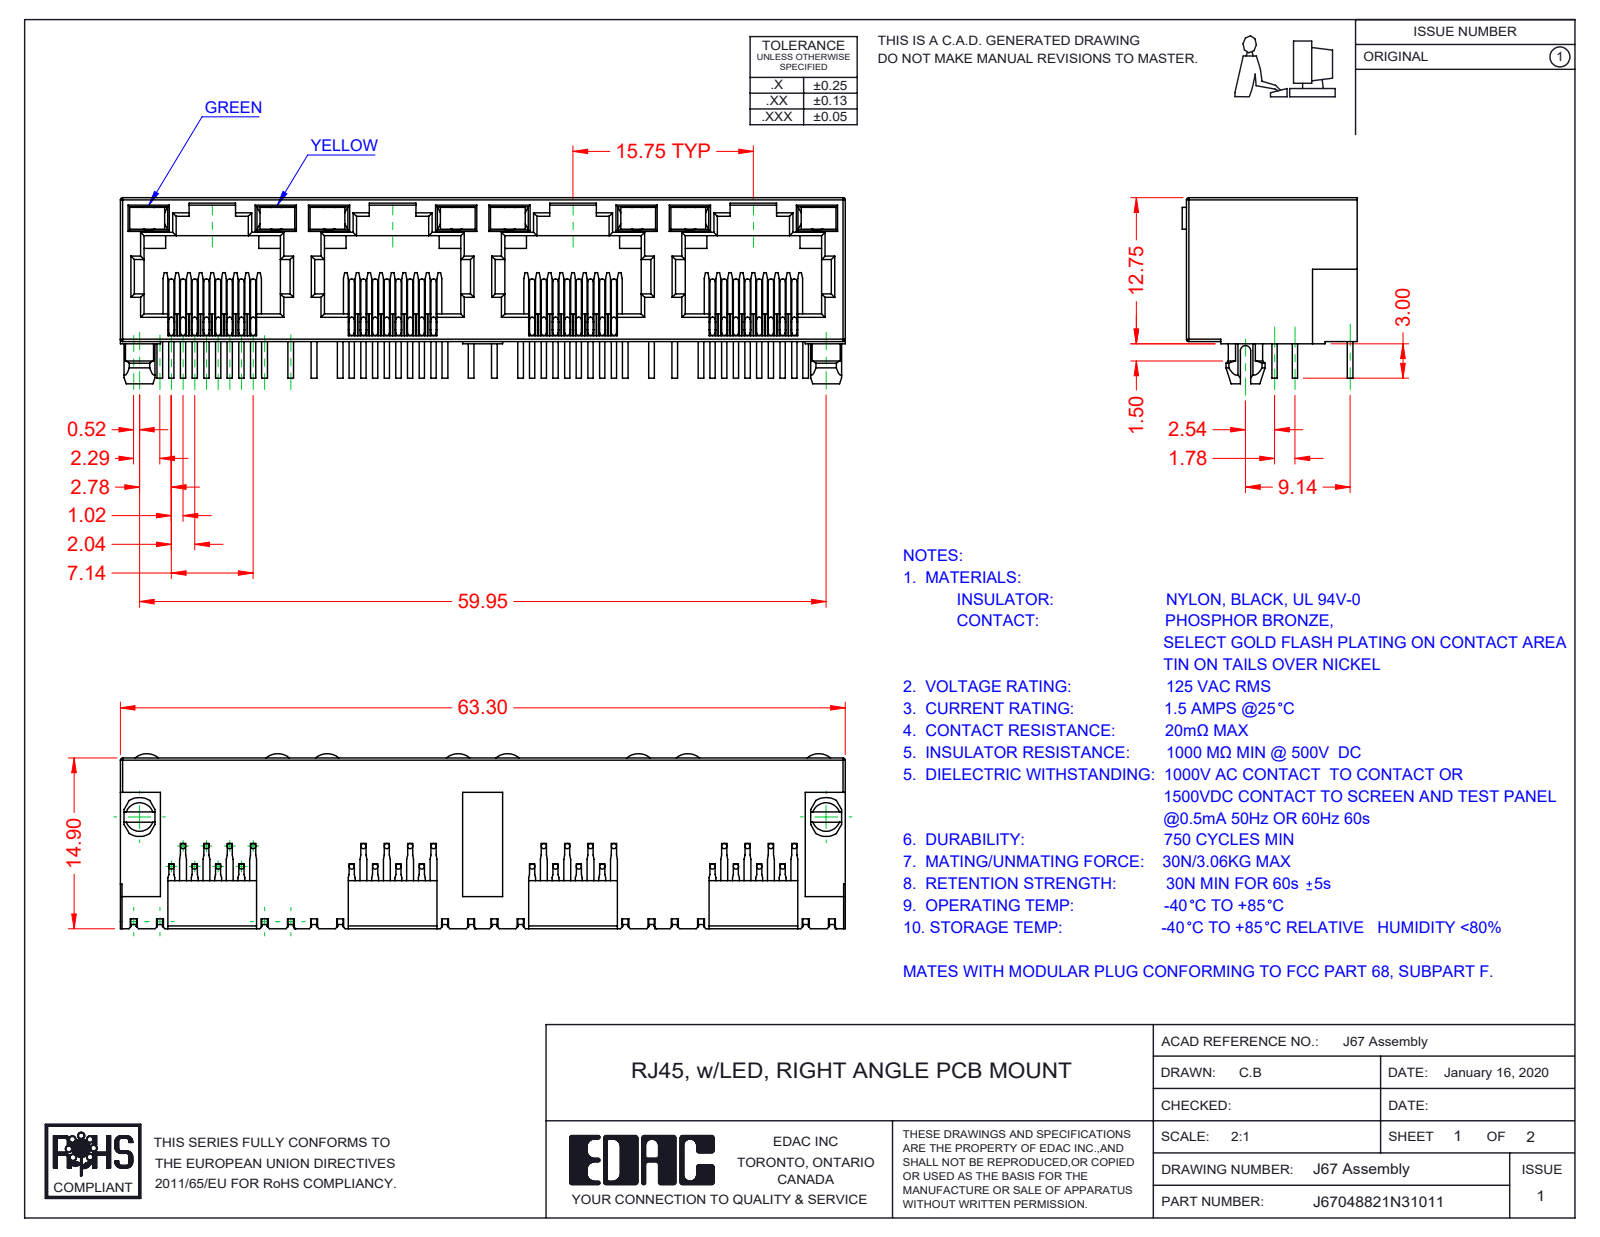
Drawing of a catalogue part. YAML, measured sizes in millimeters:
part_name: "67 Insulator; 67 LED RH_1-Yellow; 67 LED LH_3-Green; 67 Contacts (+1 more)"
step_written_by: "SolidWorks 2016 (CONFIG_CONTROL_DESIGN)"
units: millimeters
bodies: {solids: 41, faces: 2465, planar: 1781, cylindrical: 476, other: 208}
overall_size: [63.3, 16.25, 15.28]
volume: 5159
surface_area: 11573
round_bosses_or_shafts:
  - {diameter: 0.46, count: 96}
partial_cylinders:
  - {radius: 0.2, count: 66}
  - {radius: 0.3, count: 29}
  - {radius: 0.45, count: 9}
  - {radius: 1.55, count: 8}
  - {radius: 1.5, count: 2}
  - {radius: 1.7, count: 2}
  - {radius: 0.35, count: 1}
  - {radius: 1, count: 1}
face_to_face_distances: [0.5, 12.55, 1.89, 0.89, 10, 15.75, 1, 1.39, 11, 11.89]
